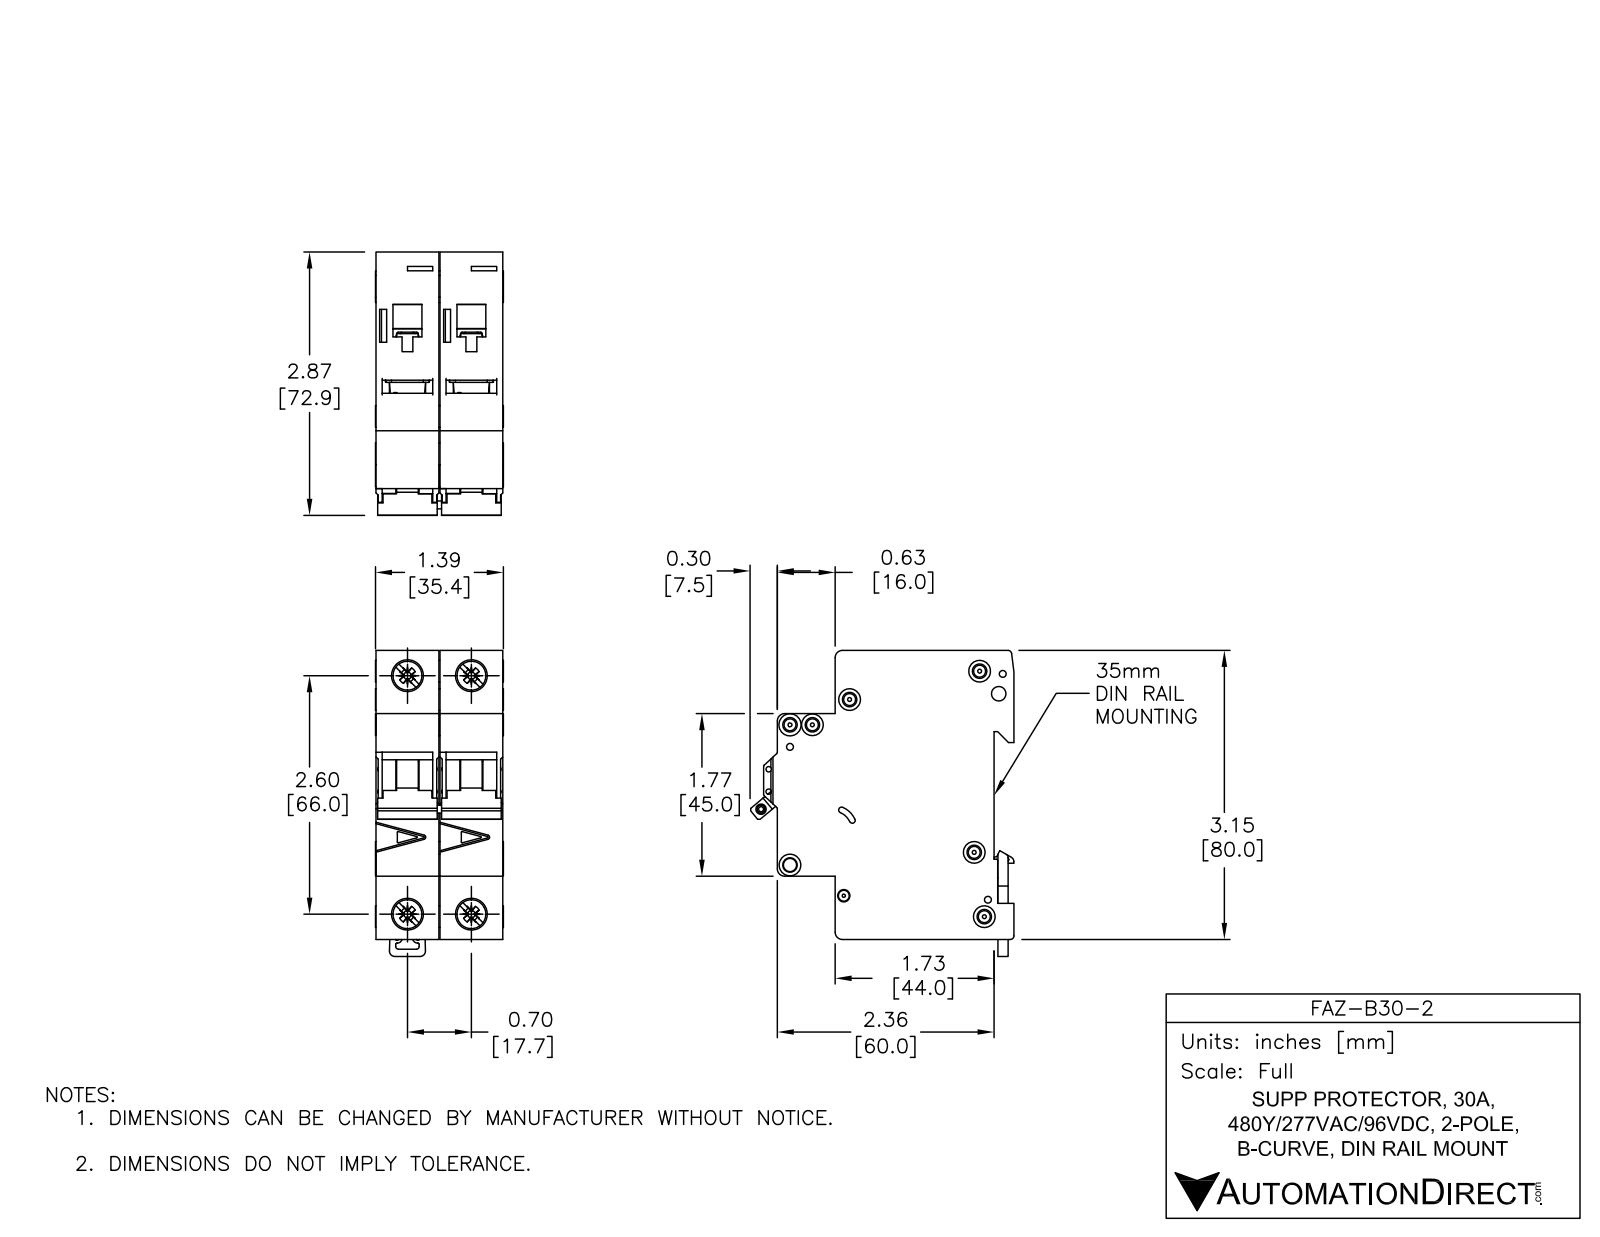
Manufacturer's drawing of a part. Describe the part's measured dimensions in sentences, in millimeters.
The part is named "FAZ-B30-2". Its 3-D file was written by "SolidWorks 2014 (AUTOMOTIVE_DESIGN)". It is 8 solids with 1104 faces: 466 planar, 396 cylindrical and 242 other. Overall it measures 84.78 by 73.04 by 35.4 millimeters. Its volume is 149 808 cubic millimeters and its surface area 38 799 square millimeters. Round holes: 6 of diameter 3.6, 3 of diameter 1.9, 2 of diameter 1.09, 2 of diameter 1.5, 2 of diameter 4, 2 of diameter 7.15, 2 of diameter 8.2, 1 of diameter 2.15, 1 of diameter 2.2, 1 of diameter 2.55, 1 of diameter 3.3, 1 of diameter 3.4. Round bosses or shafts: 4 of diameter 6, 2 of diameter 8.2, 2 of diameter 2.5. Partial cylindrical surfaces (rounded edges, fillets, slot ends): 49 of radius 0.25, 19 of radius 0.5, 10 of radius 2, 8 of radius 0.2, 8 of radius 1, 2 of radius 0.8, 2 of radius 1.8, 2 of radius 3. The main face-to-face distances are 17.7, 17.5, 35.2, 79.48, 5.5, 49.5, 44, 65.5, 60, 16. The hole center spacings are 6.2, 13.64, 17.7, 66, 68.33, 4.81, 5.19, 5.61.
